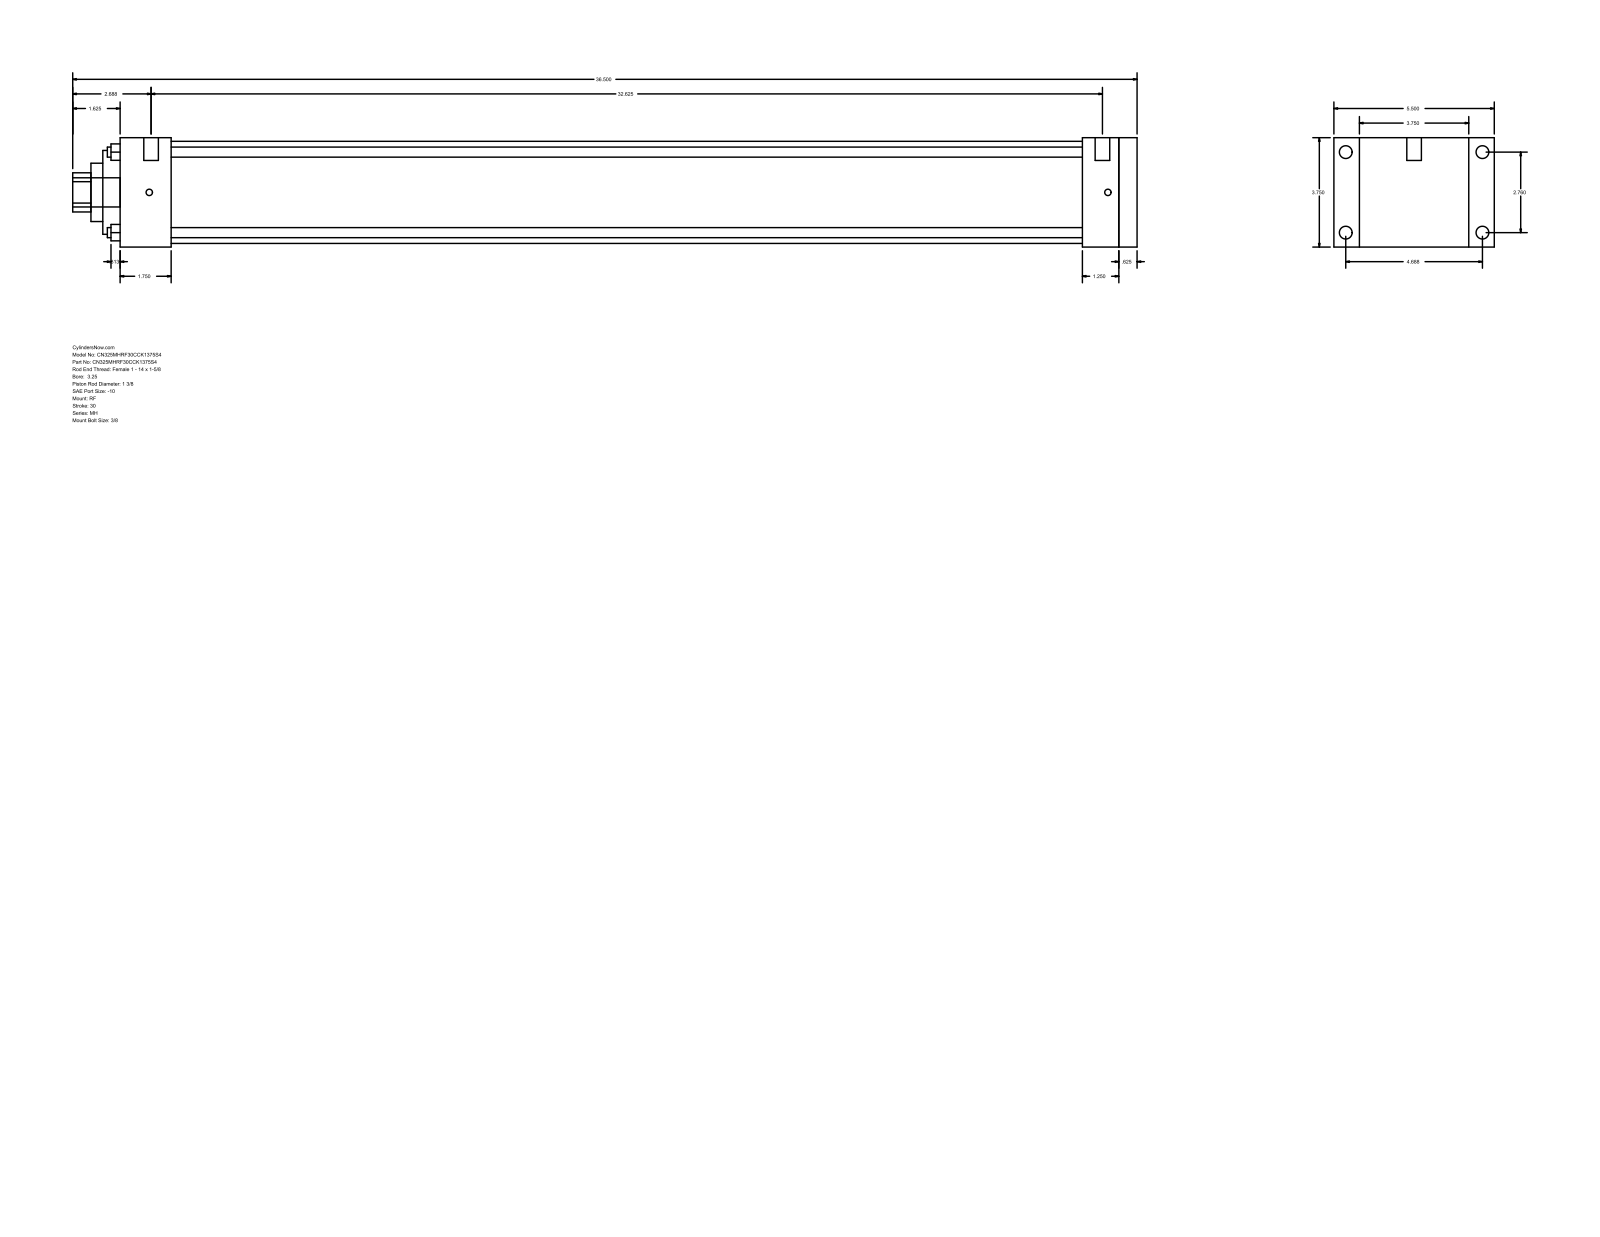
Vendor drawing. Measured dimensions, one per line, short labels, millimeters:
name: MH_RF__0325_1.375
written by: GSSL Pune (CONFIG_CONTROL_DESIGN)
unit: mm
bodies: 0 solids, 94 faces (65 planar, 29 cylindrical, 0 other)
size: 927.1 × 139.7 × 95.25
holes: 4× ⌀8.76, 1× ⌀34.92, 1× ⌀50.8, 1× ⌀73.03, 1× ⌀88.9
bosses: 4× ⌀11.13, 4× ⌀5.56, 2× ⌀12.7, 1× ⌀25.4
rounds: 1× R17.06
face distances: 95.24, 885.83, 869.96, 15.87, 22.23, 117.47, 44.45, 825.51, 841.38, 838.21
hole spacings: 49.57, 70.1, 99.14
